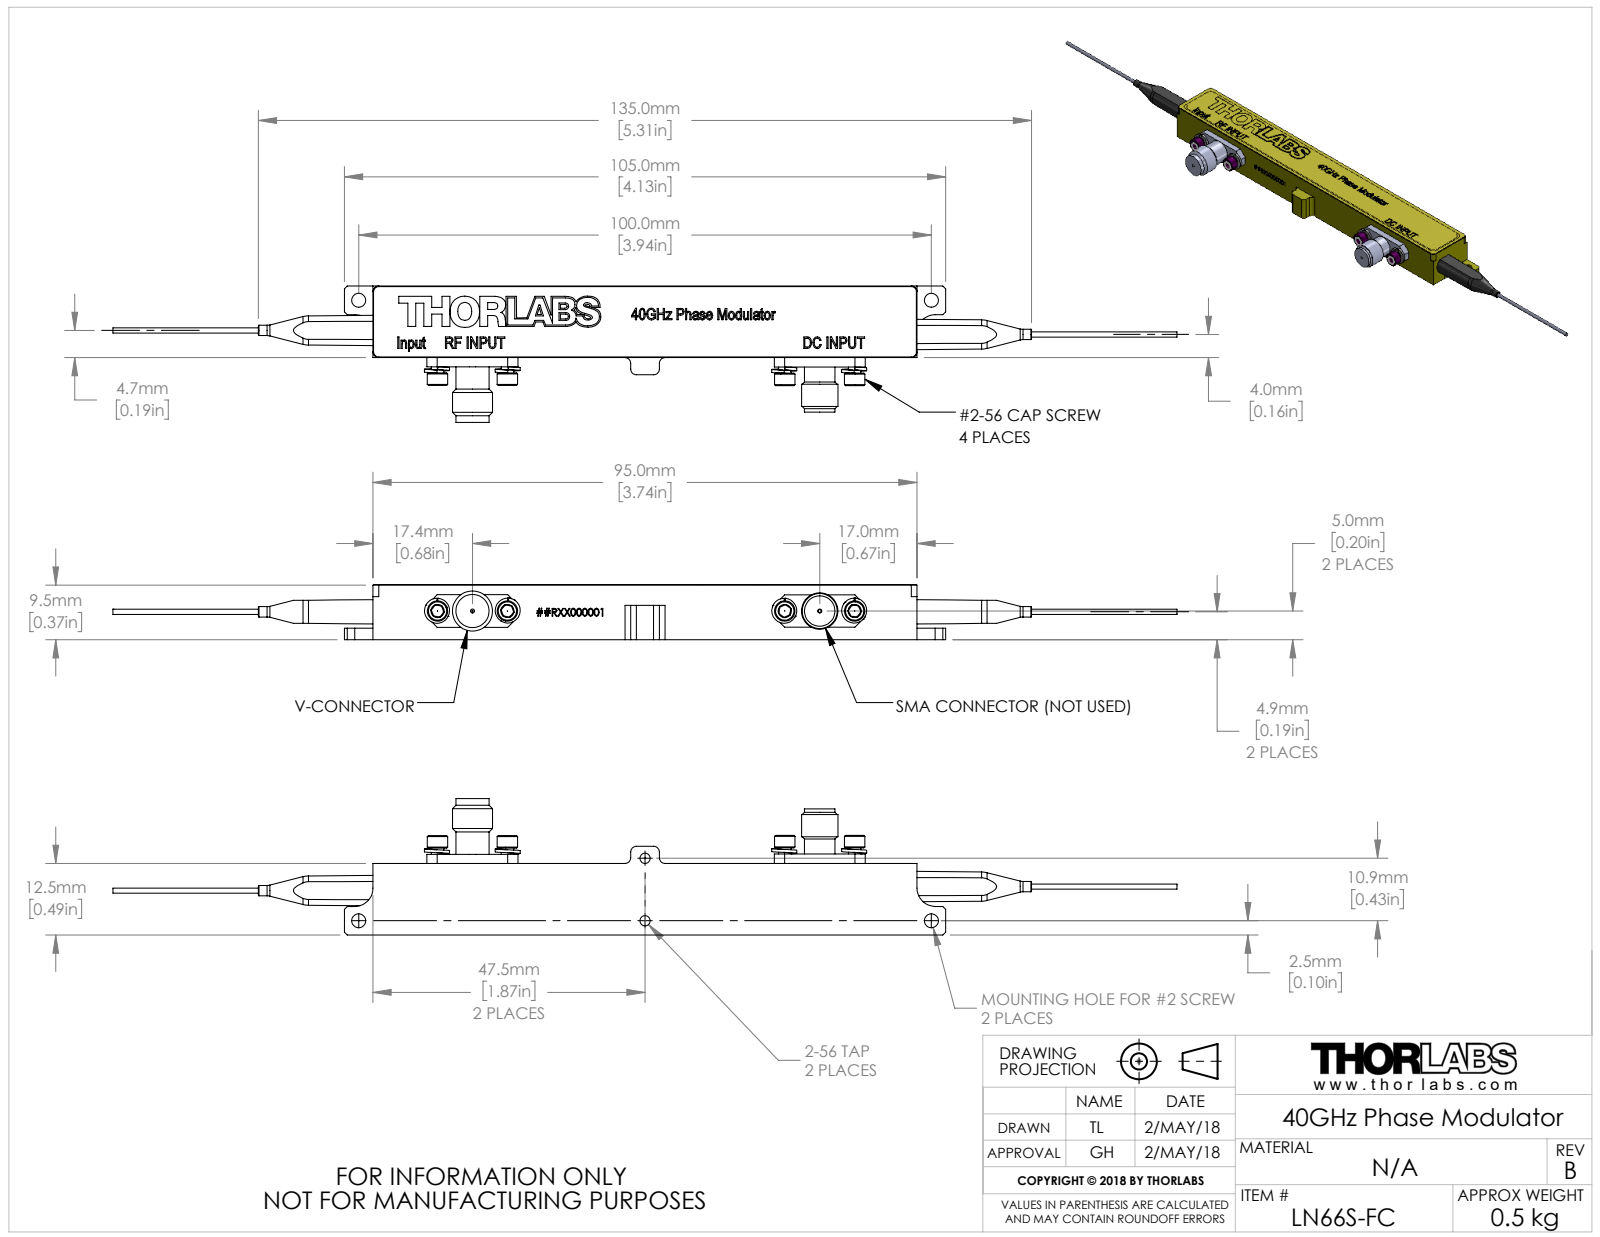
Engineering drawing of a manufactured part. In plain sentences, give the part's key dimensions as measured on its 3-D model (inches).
The part is named "20870-E0W". Its 3-D file was written by "SolidWorks 2016 (CONFIG_CONTROL_DESIGN)". It is 0 solids with 583 faces: 350 planar, 62 cylindrical and 171 other. Overall it measures 7.315 by 0.937 by 0.379 inches. Round holes: 2 of diameter 0.028, 2 of diameter 0.07, 2 of diameter 0.096. Round bosses or shafts: 4 of diameter 0.14, 4 of diameter 0.086, 2 of diameter 0.071, 2 of diameter 0.035, 1 of diameter 0.276, 1 of diameter 0.25, 1 of diameter 0.228, 1 of diameter 0.209. Partial cylindrical surfaces (rounded edges, fillets, slot ends): 8 of radius 0.039, 4 of radius 0.035, 2 of radius 0.125. The main face-to-face distances are 0.379, 0.492, 0.374, 0.377, 3.74, 0.065, 0.557, 0.298, 0.295, 0.555. The hole center spacings are 1.969, 2.015, 0.429, 2.387, 3.937.
